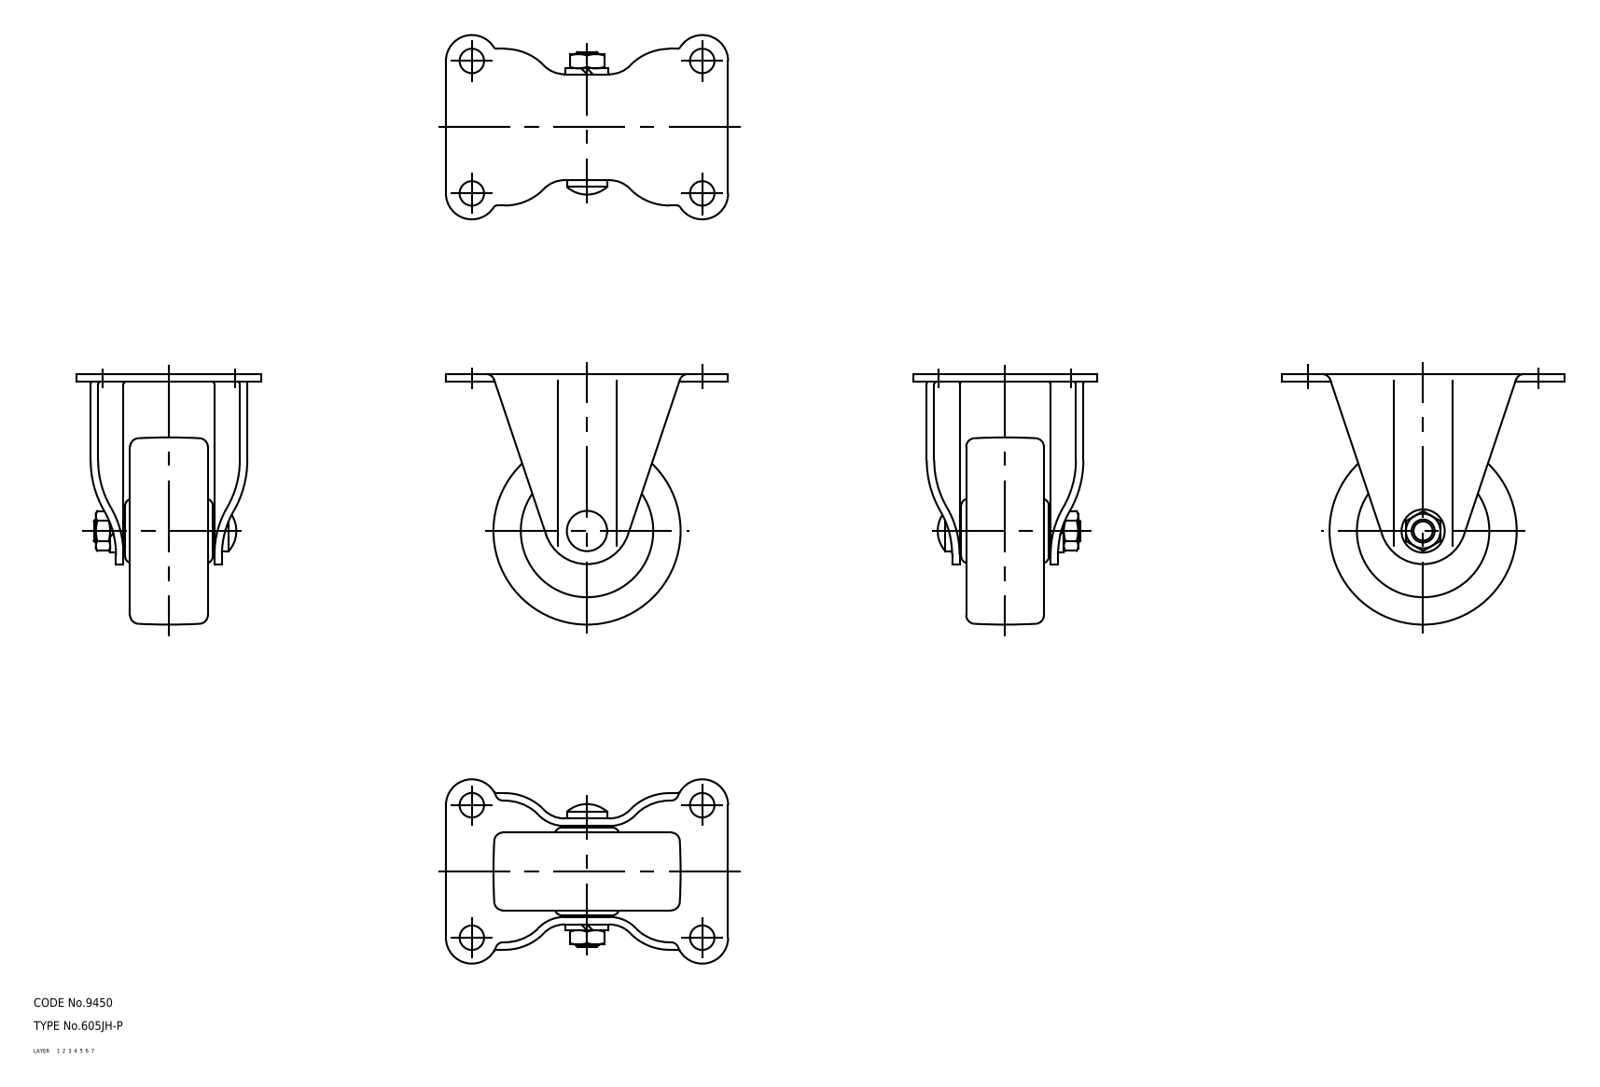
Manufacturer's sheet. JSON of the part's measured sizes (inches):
{"part_name": "wheel; axle; No_605JH_P_16027_36", "step_written_by": "CADfix (AUTOMOTIVE_DESIGN)", "units": "inches", "bodies": {"solids": 3, "faces": 204, "planar": 0, "cylindrical": 0, "other": 204}, "overall_size": [3.858, 3.425, 2.52], "volume_in3": 6.301, "surface_area_in2": 59.51}
